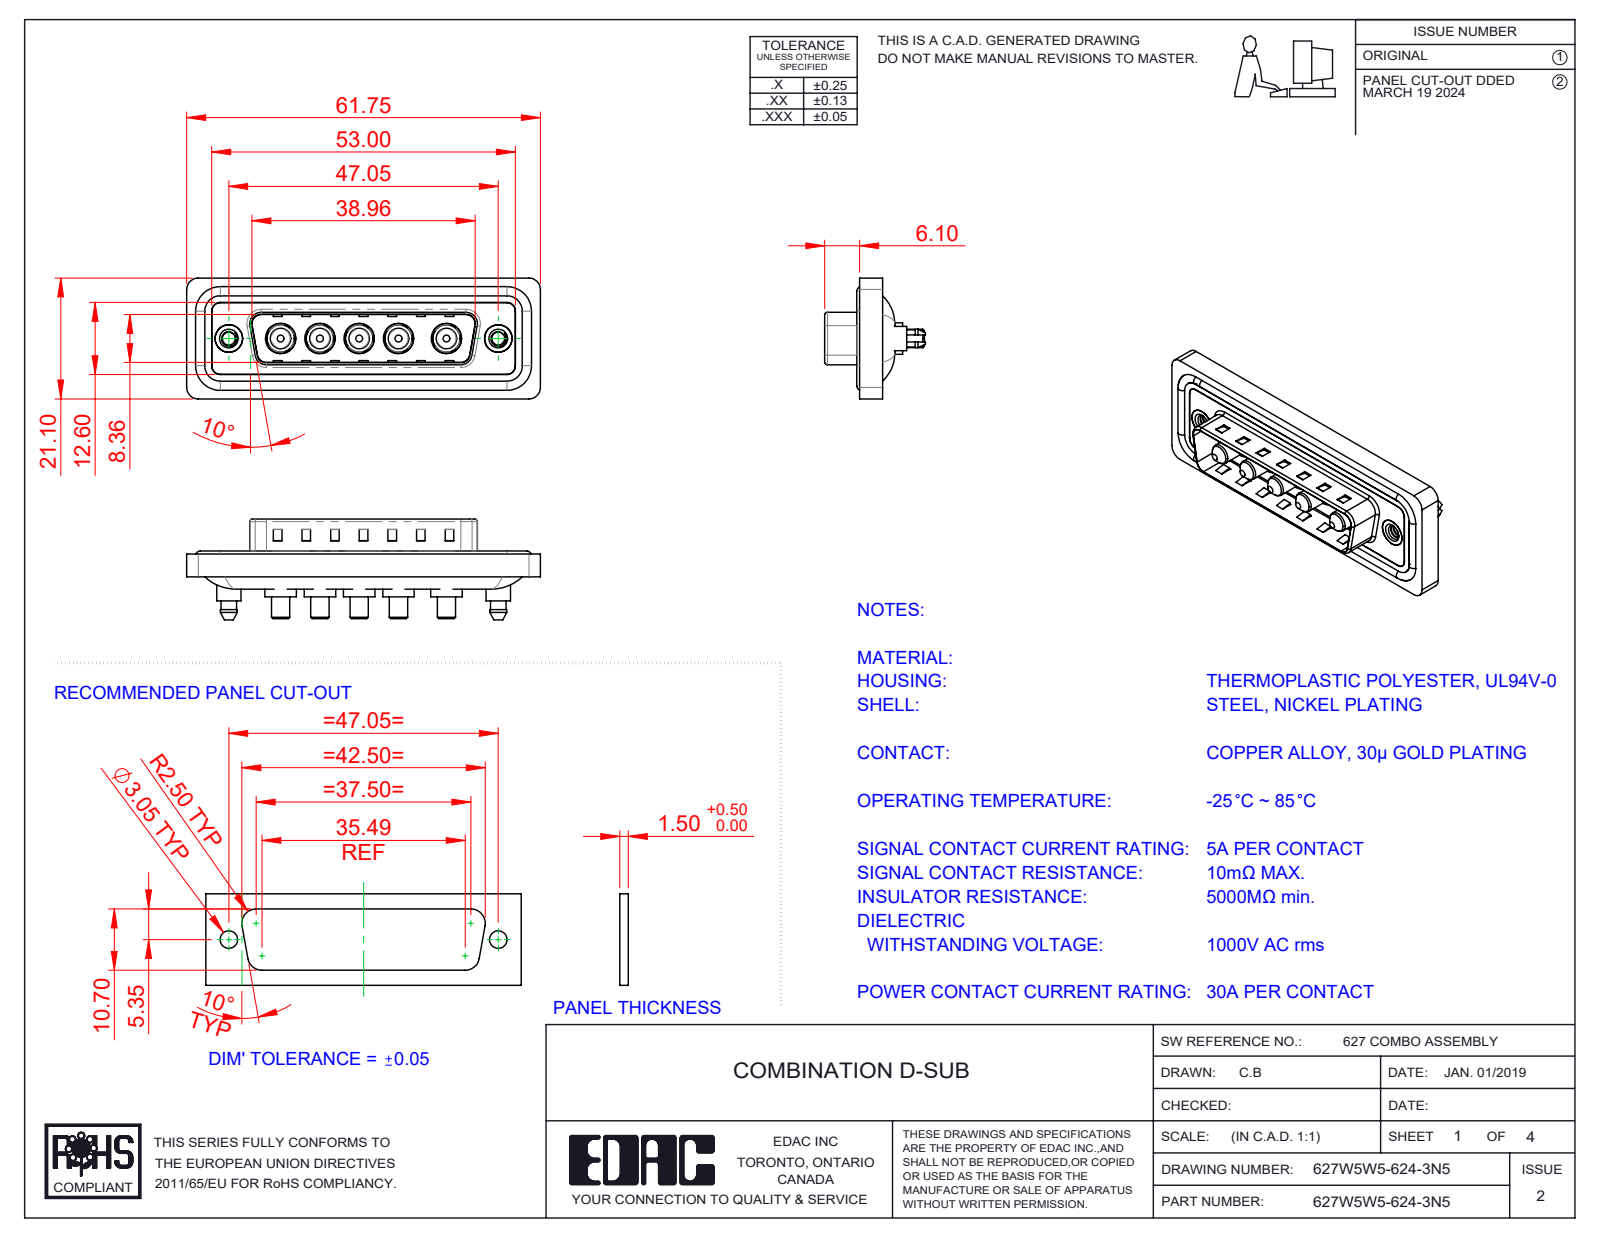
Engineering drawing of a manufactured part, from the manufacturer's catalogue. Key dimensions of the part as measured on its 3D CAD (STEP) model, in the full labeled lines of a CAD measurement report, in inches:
Part name (STEP PRODUCT): 627W5W5-624-3N5; 627Combo Waterproof Housing_25 Contacts; 627Combo Threaded Boardlock_5; Power Pin_30A S (+3 more)
STEP written by: SolidWorks 2023 (CONFIG_CONTROL_DESIGN)
Units: inches
Bodies: 17 solids, 728 faces (275 planar, 315 cylindrical, 138 other)
Overall size (bounding box): 2.431 × 0.831 × 0.693
Volume: 0.466 in³ · Surface area: 18.84 in²
Round holes (diameter × count): ⌀0.191 ×5, ⌀0.209 ×5, ⌀0.089 ×2, ⌀0.157 ×2, ⌀0.189 ×2, ⌀0.197 ×2
Round bosses / shafts (diameter × count): ⌀0.217 ×5, ⌀0.205 ×5, ⌀0.187 ×5, ⌀0.148 ×5, ⌀0.142 ×5, ⌀0.126 ×5, ⌀0.063 ×4, ⌀0.213 ×2
Partial cylindrical surfaces — rounded edges, fillets, slot ends (radius × count): R0.059 ×24, R0.079 ×18, R0.063 ×10, R0.02 ×8, R0.083 ×5, R0.01 ×4, R0.024 ×4, R0.026 ×4
Main face-to-face distances: 0.016, 0.059, 0.122, 0.043, 0.02, 0.063, 0.114, 0.032, 0.377, 0.222
Hole centre spacings: 0.27, 0.356, 0.541, 1.496, 0.27, 0.33, 0.33, 0.356
